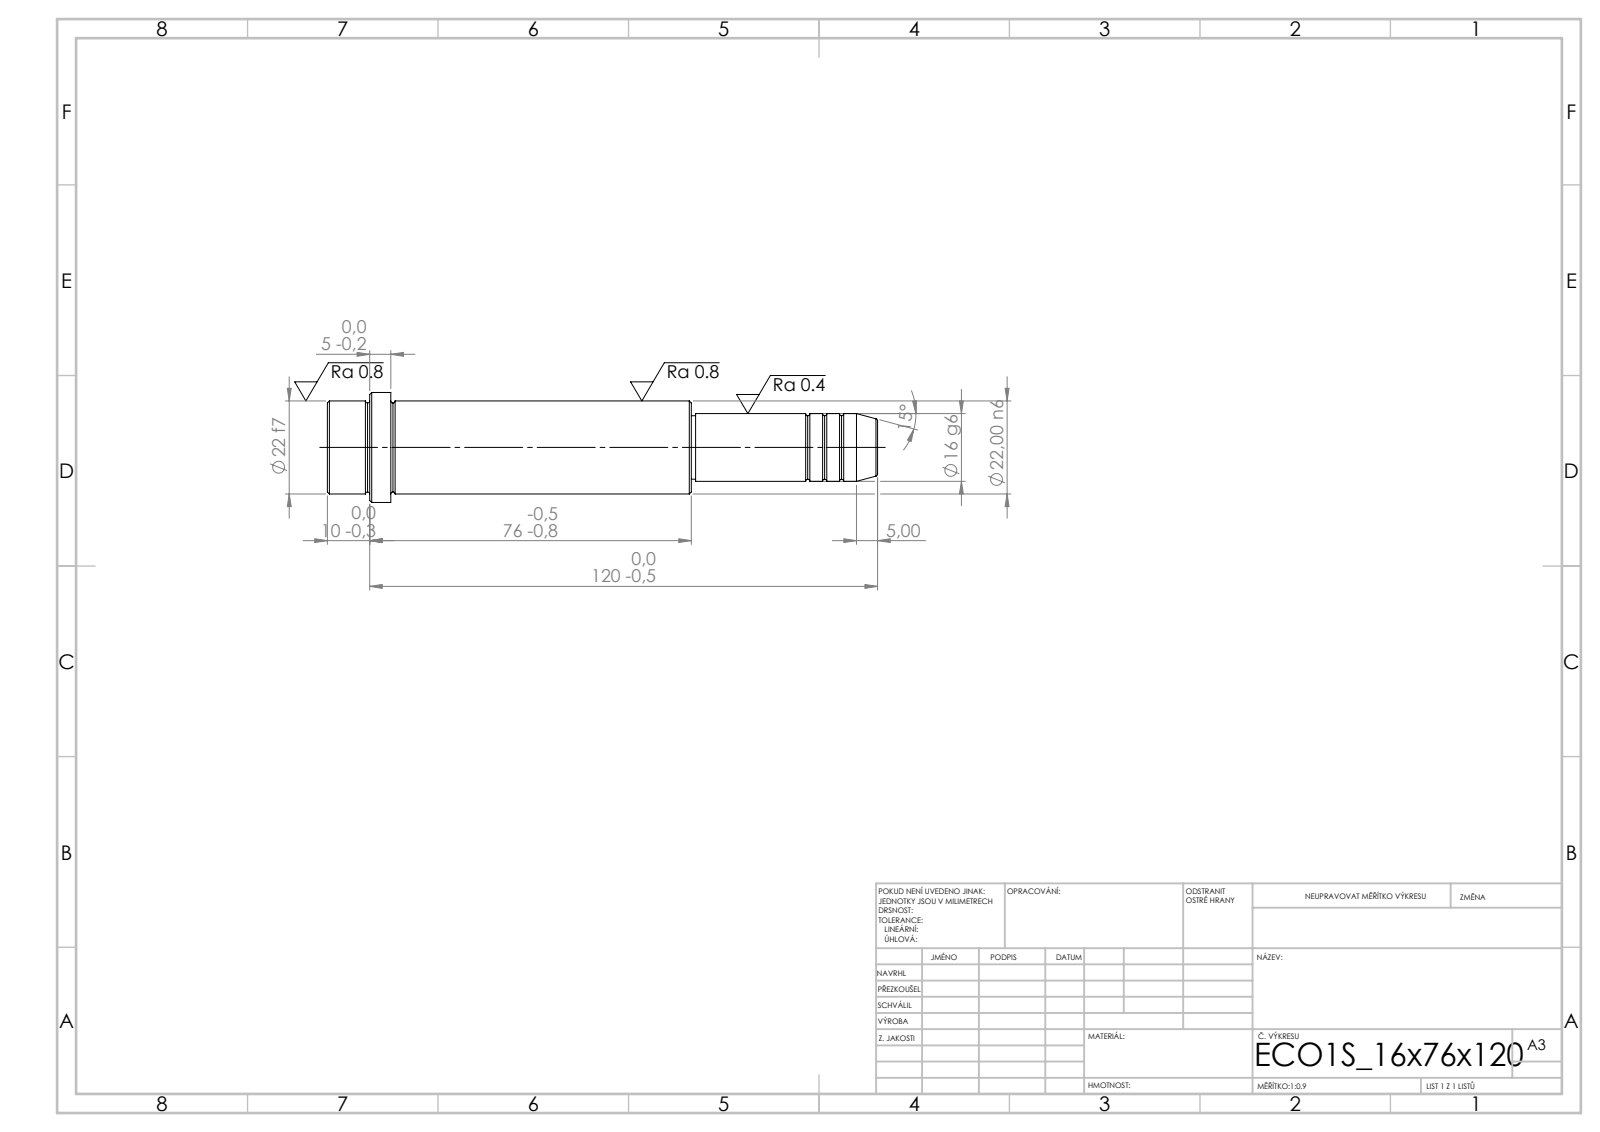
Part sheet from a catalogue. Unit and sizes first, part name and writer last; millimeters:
Units: millimetres
Overall size (bounding box): 130 × 26 × 26
Round bosses / shafts (diameter × count): ⌀26 ×1, ⌀22 ×1, ⌀16 ×1, ⌀15 ×1
Main face-to-face distances: 86, 71, 15, 44, 115, 130, 120, 76, 5, 10
Volume: 41 970 mm³ · Surface area: 9 330 mm²
Bodies: 1 solid, 52 faces (6 planar, 16 cylindrical, 30 other)
STEP written by: SolidWorks 2019 (CONFIG_CONTROL_DESIGN)
